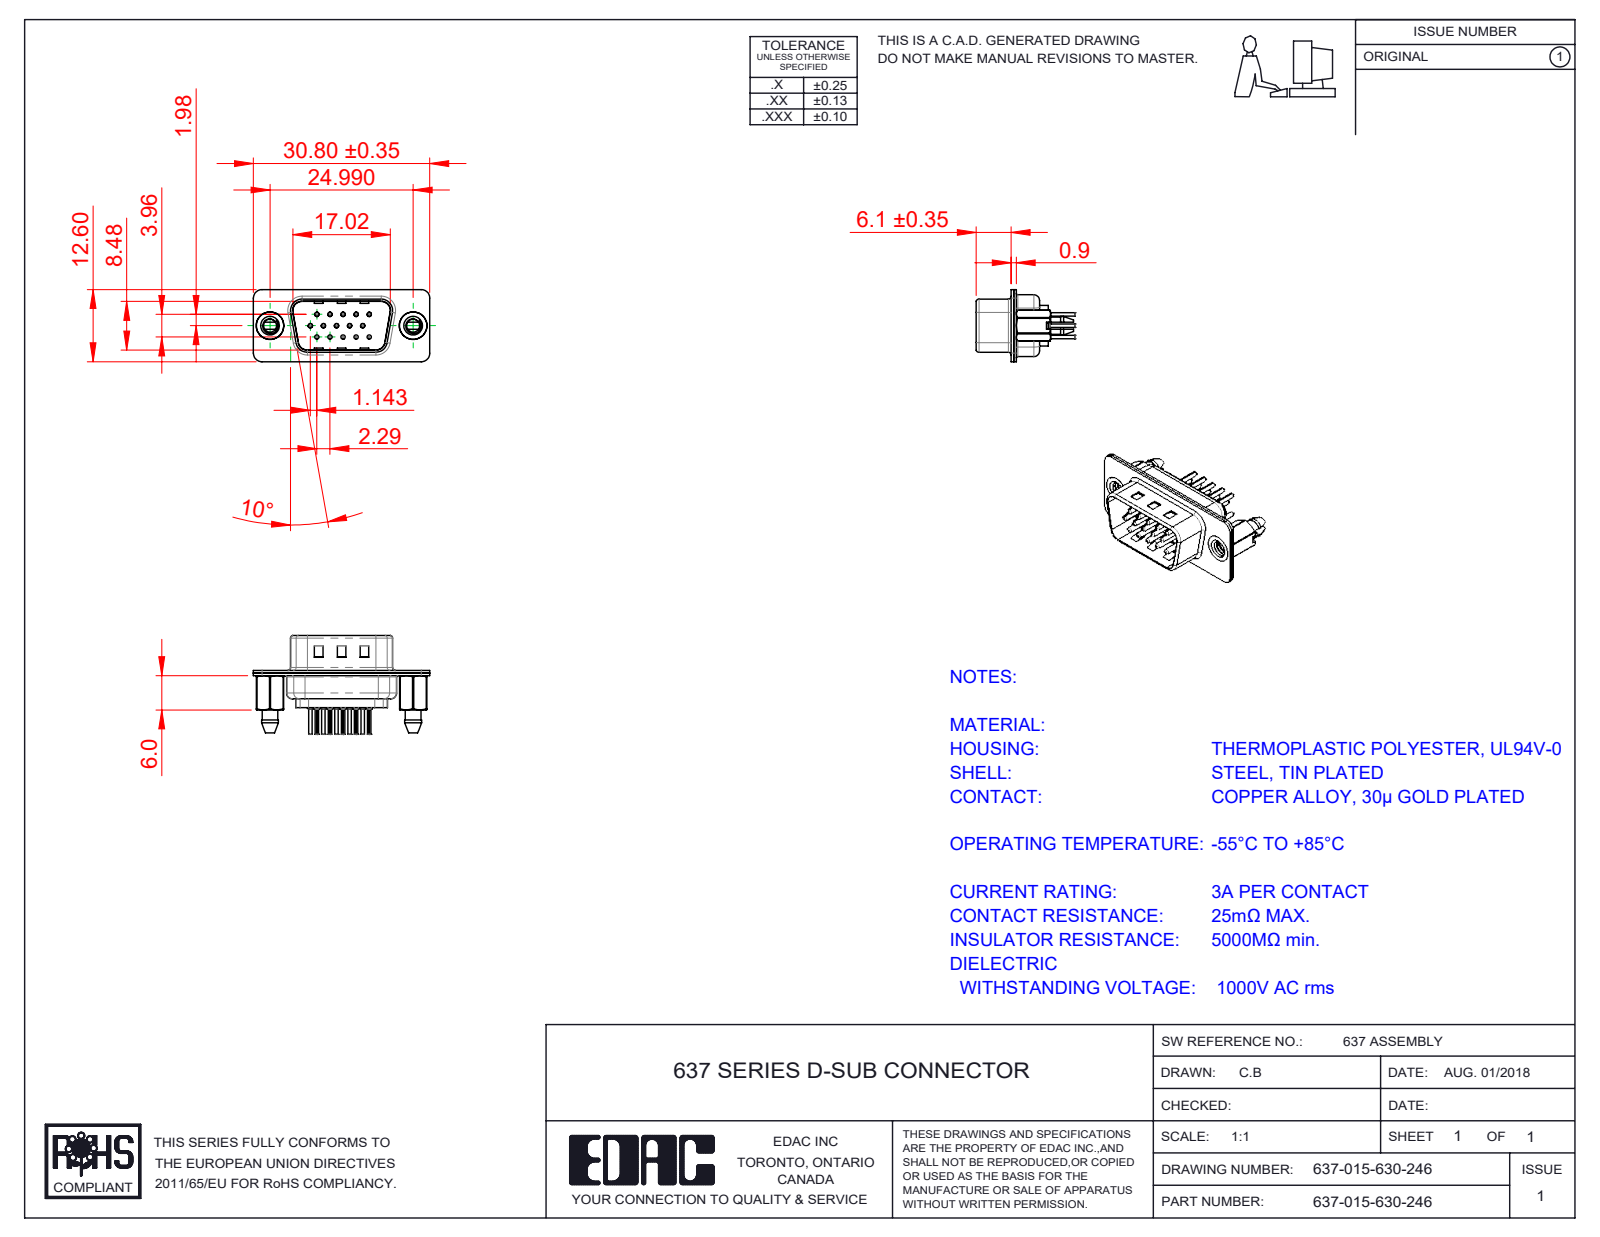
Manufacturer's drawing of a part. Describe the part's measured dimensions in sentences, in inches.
The part is named "637 Contact Row 3_30; 637 Contact Row 2_30; 637-015-630-246; 637 Housing_15 Contacts (+4 more)". Its 3-D file was written by "SolidWorks 2020 (CONFIG_CONTROL_DESIGN)". It is 20 solids with 1878 faces: 499 planar, 716 cylindrical and 663 other. Overall it measures 1.213 by 0.679 by 0.496 inches. Its volume is 0.087 cubic inches and its surface area 7.646 square inches. Round holes: 15 of diameter 0.008, 15 of diameter 0.014, 15 of diameter 0.043, 15 of diameter 0.063, 2 of diameter 0.089, 2 of diameter 0.157, 2 of diameter 0.189. Round bosses or shafts: 15 of diameter 0.079, 15 of diameter 0.059, 15 of diameter 0.03, 15 of diameter 0.024, 2 of diameter 0.193. Partial cylindrical surfaces (rounded edges, fillets, slot ends): 30 of radius 0.004, 18 of radius 0.059, 12 of radius 0.079, 8 of radius 0.02, 6 of radius 0.063, 4 of radius 0.01, 4 of radius 0.022, 4 of radius 0.028. The main face-to-face distances are 0.018, 0.016, 0.035, 0.028, 0.35, 0.334, 0.041, 0.256, 0.179, 0.012. The hole center spacings are 0.156, 0.09, 0.18, 0.09, 0.238, 0.27, 0.312, 0.238.
